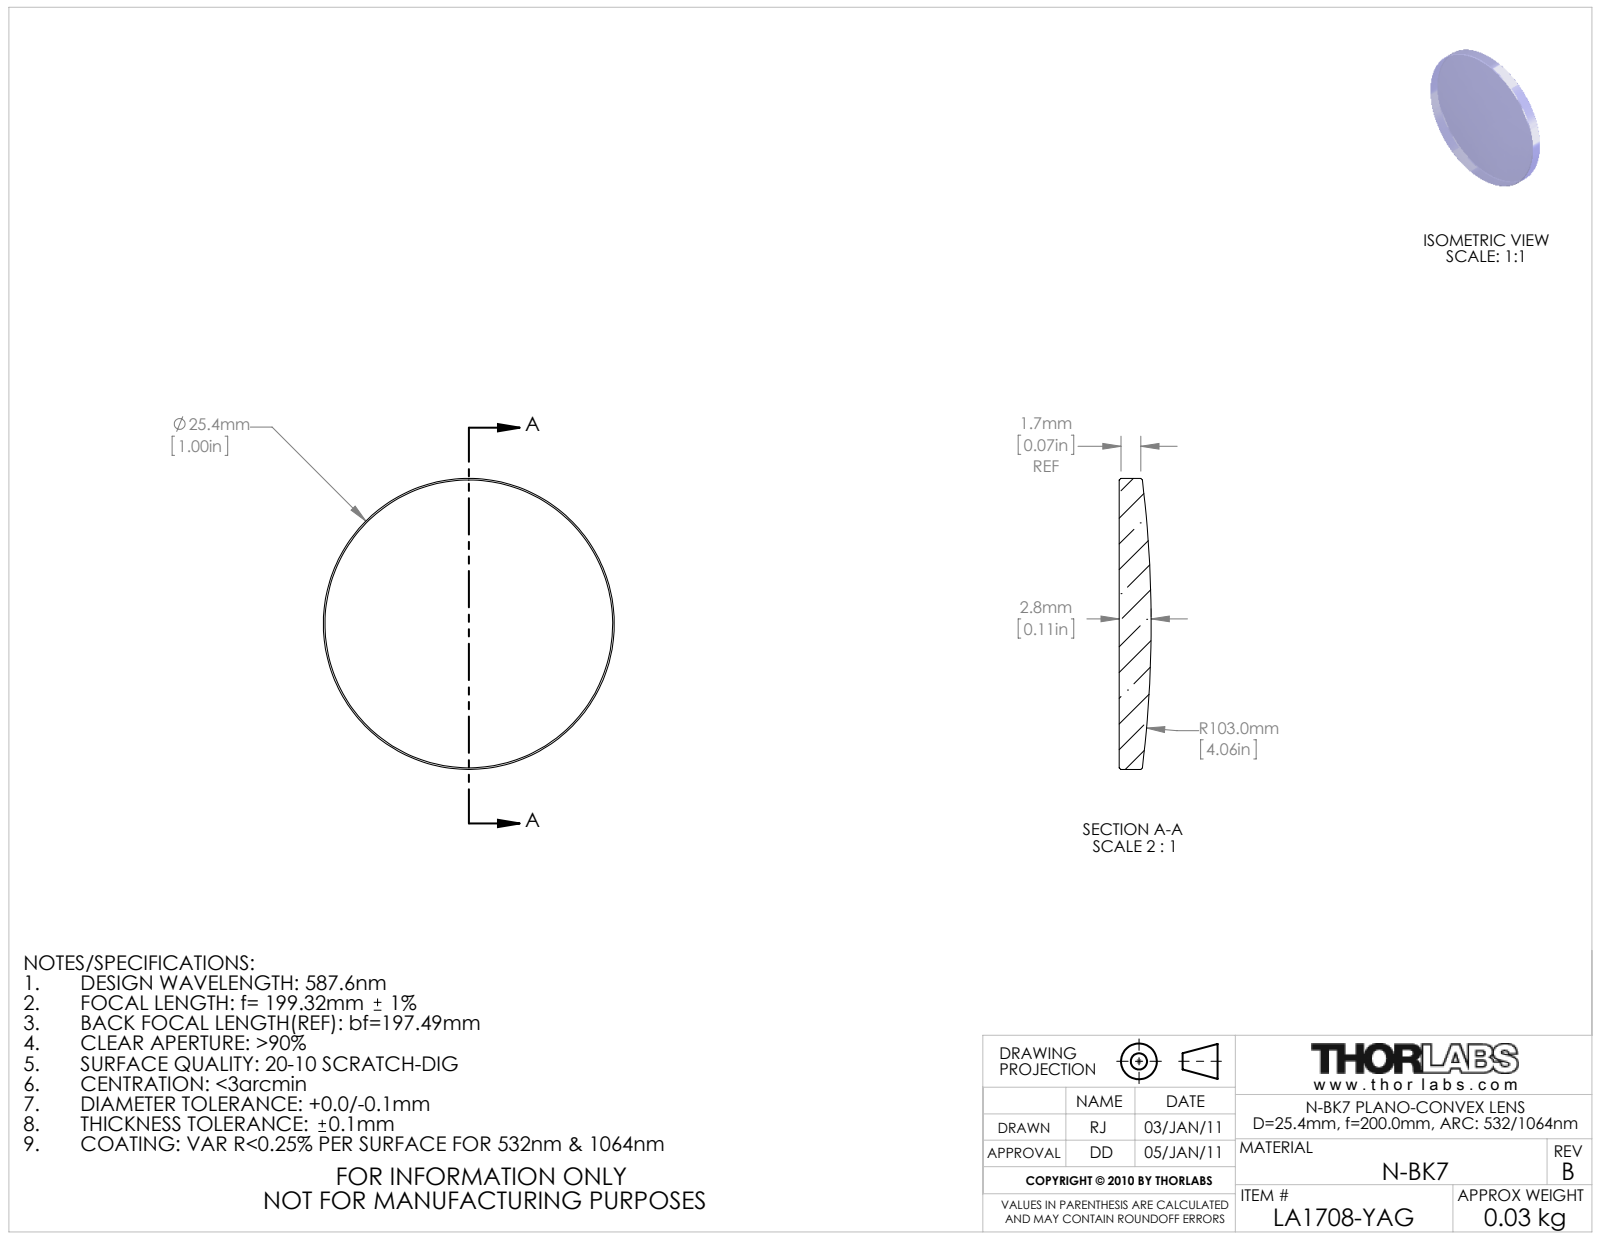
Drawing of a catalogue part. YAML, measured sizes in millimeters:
part_name: "21797-E0W"
step_written_by: "SolidWorks 2011 (AUTOMOTIVE_DESIGN)"
units: millimeters
bodies: {solids: 0, faces: 9, planar: 1, cylindrical: 2, other: 6}
overall_size: [25.4, 25.4, 2.78]
round_bosses_or_shafts:
  - {diameter: 25.4, count: 1}
